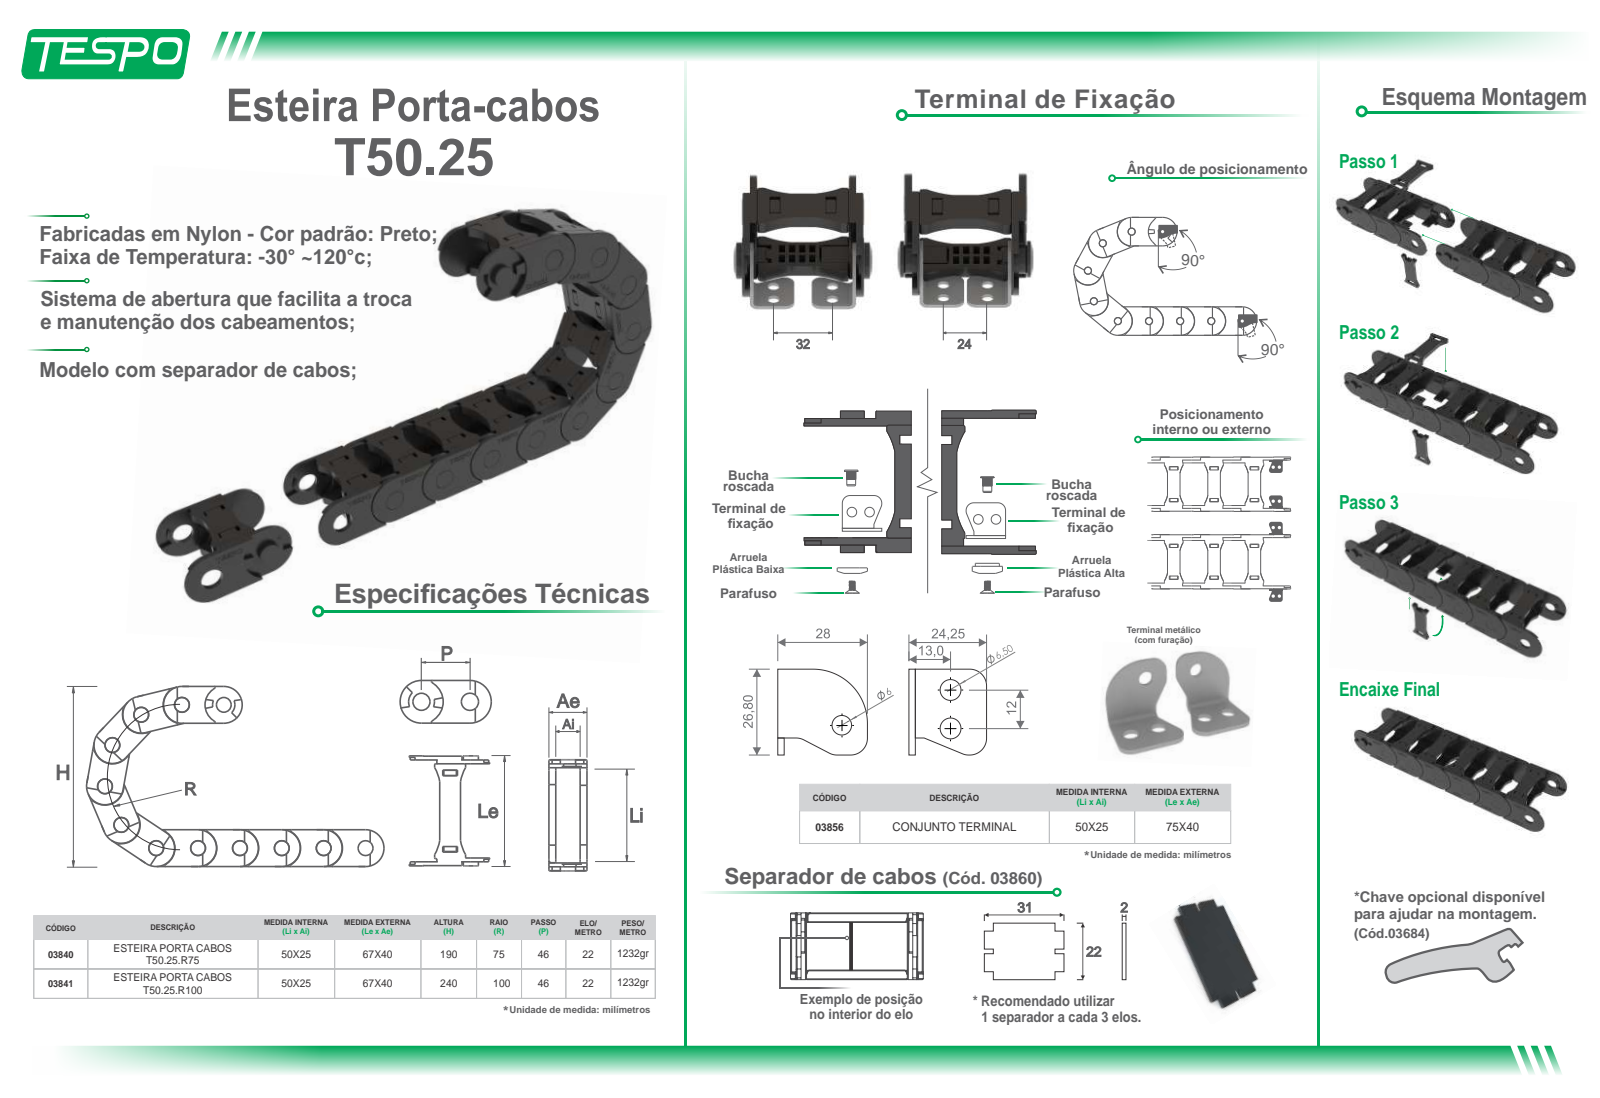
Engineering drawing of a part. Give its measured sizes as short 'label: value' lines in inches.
written by: ST-DEVELOPER v15 (AUTOMOTIVE_DESIGN)
unit: in
bodies: 4 solids, 155 faces (92 planar, 0 cylindrical, 63 other)
size: 3.366 × 2.629 × 1.575
volume: 2.87 in³; area: 39.86 in²
face distances: 0.159, 2.287, 2.127, 0.319, 2.446, 1.575, 1.968, 0.283, 1.291, 2.606
